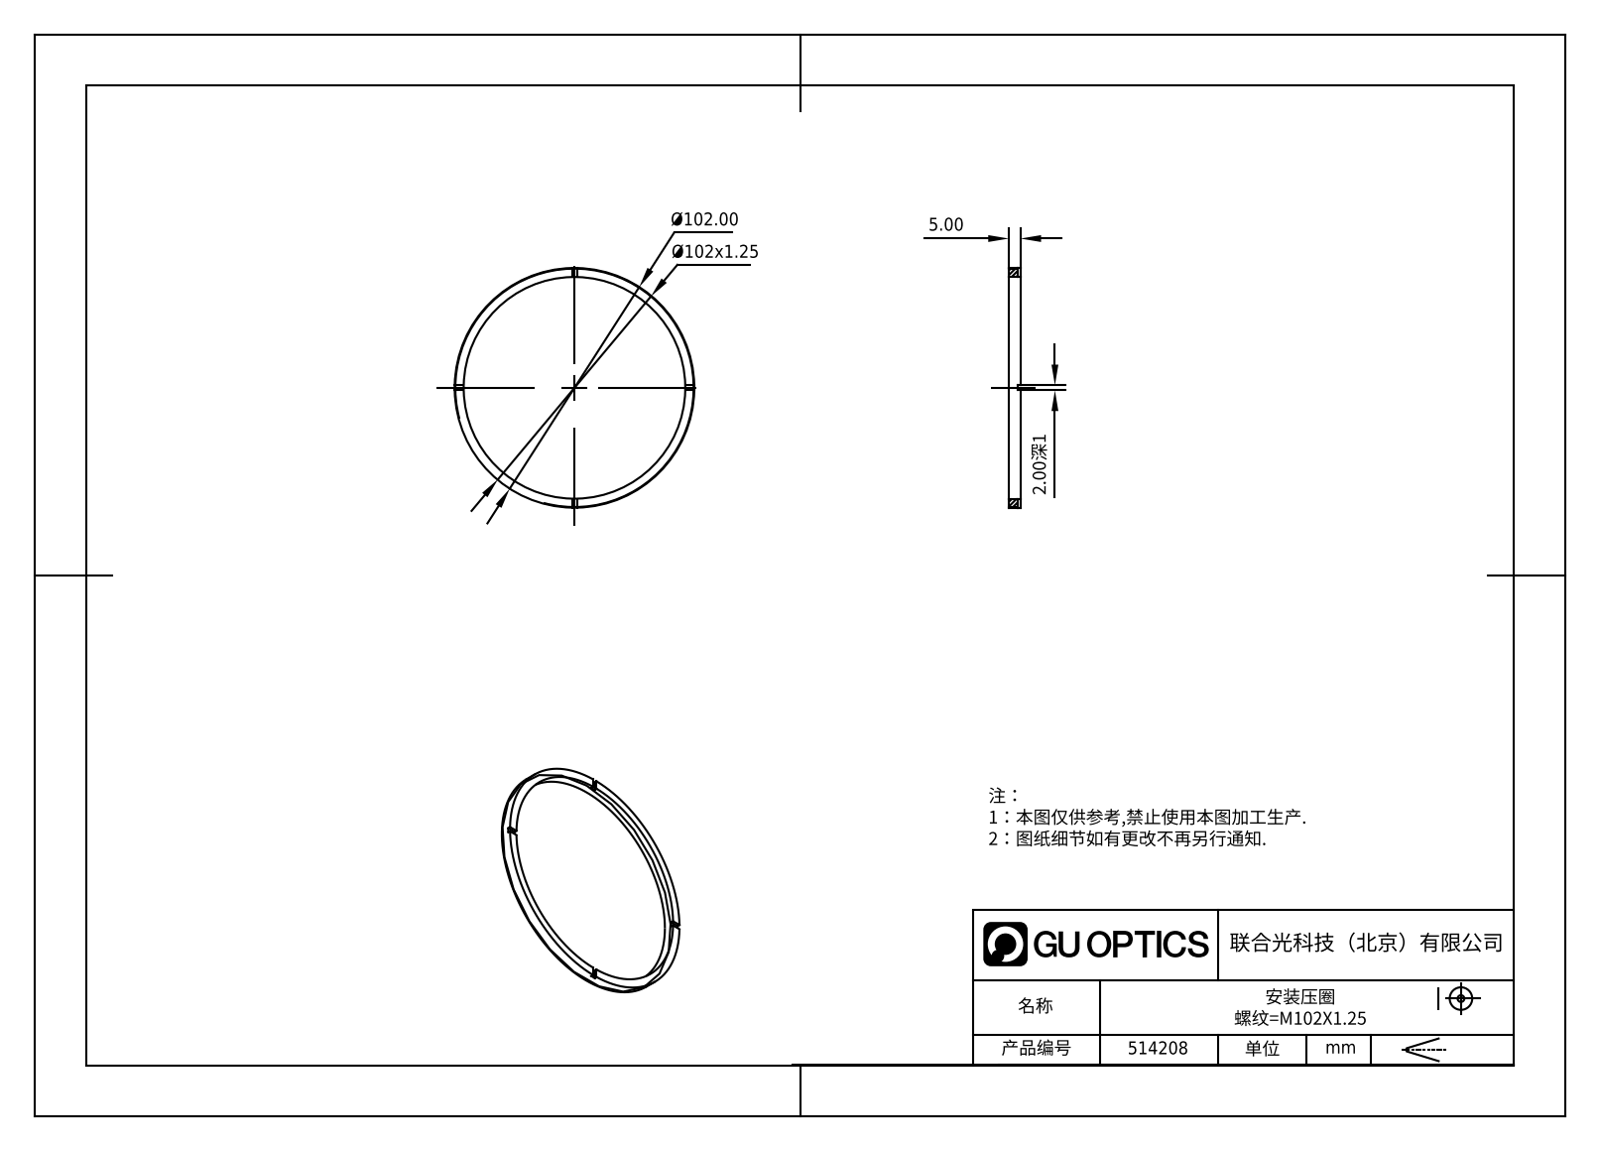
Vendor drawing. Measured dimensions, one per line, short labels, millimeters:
name: 514208
written by: SolidWorks 2020 (CONFIG_CONTROL_DESIGN)
unit: mm
bodies: 1 solid, 21 faces (17 planar, 4 cylindrical, 0 other)
size: 102 × 102 × 5
volume: 6 126 mm³; area: 5 558 mm²
holes: 1× ⌀94
bosses: 1× ⌀102
face distances: 5, 4, 1, 2
